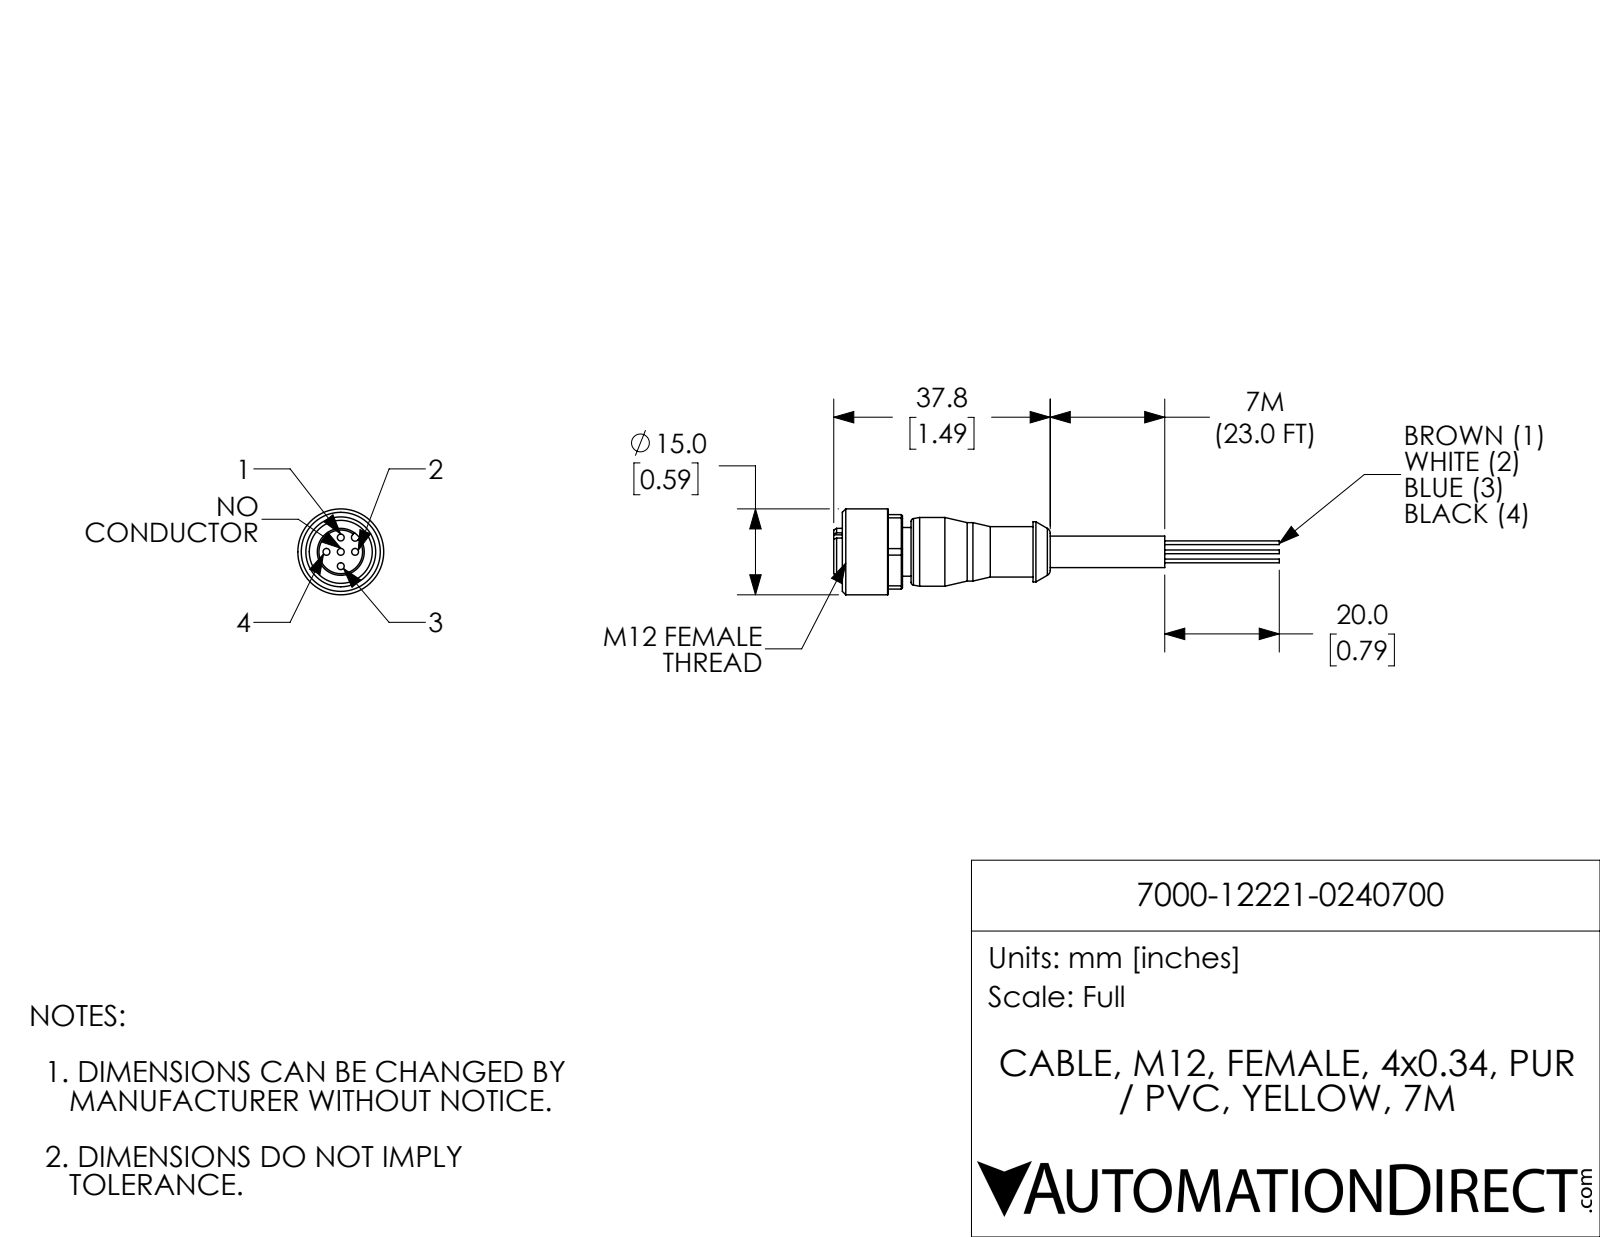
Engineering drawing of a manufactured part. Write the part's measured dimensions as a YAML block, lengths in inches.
part_name: "7000-12221-0240700"
step_written_by: "SolidWorks 2017 (AUTOMOTIVE_DESIGN)"
units: inches
bodies: {solids: 1, faces: 103, planar: 33, cylindrical: 43, other: 27}
overall_size: [3.063, 0.591, 0.591]
volume: 0.247
surface_area: 4.386
round_holes:
  - {diameter: 0.047, count: 5}
  - {diameter: 0.433, count: 1}
round_bosses_or_shafts:
  - {diameter: 0.026, count: 4}
  - {diameter: 0.591, count: 1}
  - {diameter: 0.472, count: 1}
  - {diameter: 0.413, count: 1}
  - {diameter: 0.402, count: 1}
  - {diameter: 0.346, count: 1}
  - {diameter: 0.335, count: 1}
  - {diameter: 0.323, count: 1}
partial_cylinders:
  - {radius: 0.026, count: 1}
  - {radius: 0.283, count: 1}
face_to_face_distances: [0.472, 0.059, 0.118, 0.512, 0.354, 1.016, 0.295, 0.413, 0.098, 0.531]
hole_center_spacings: [0.098, 0.139, 0.197]
